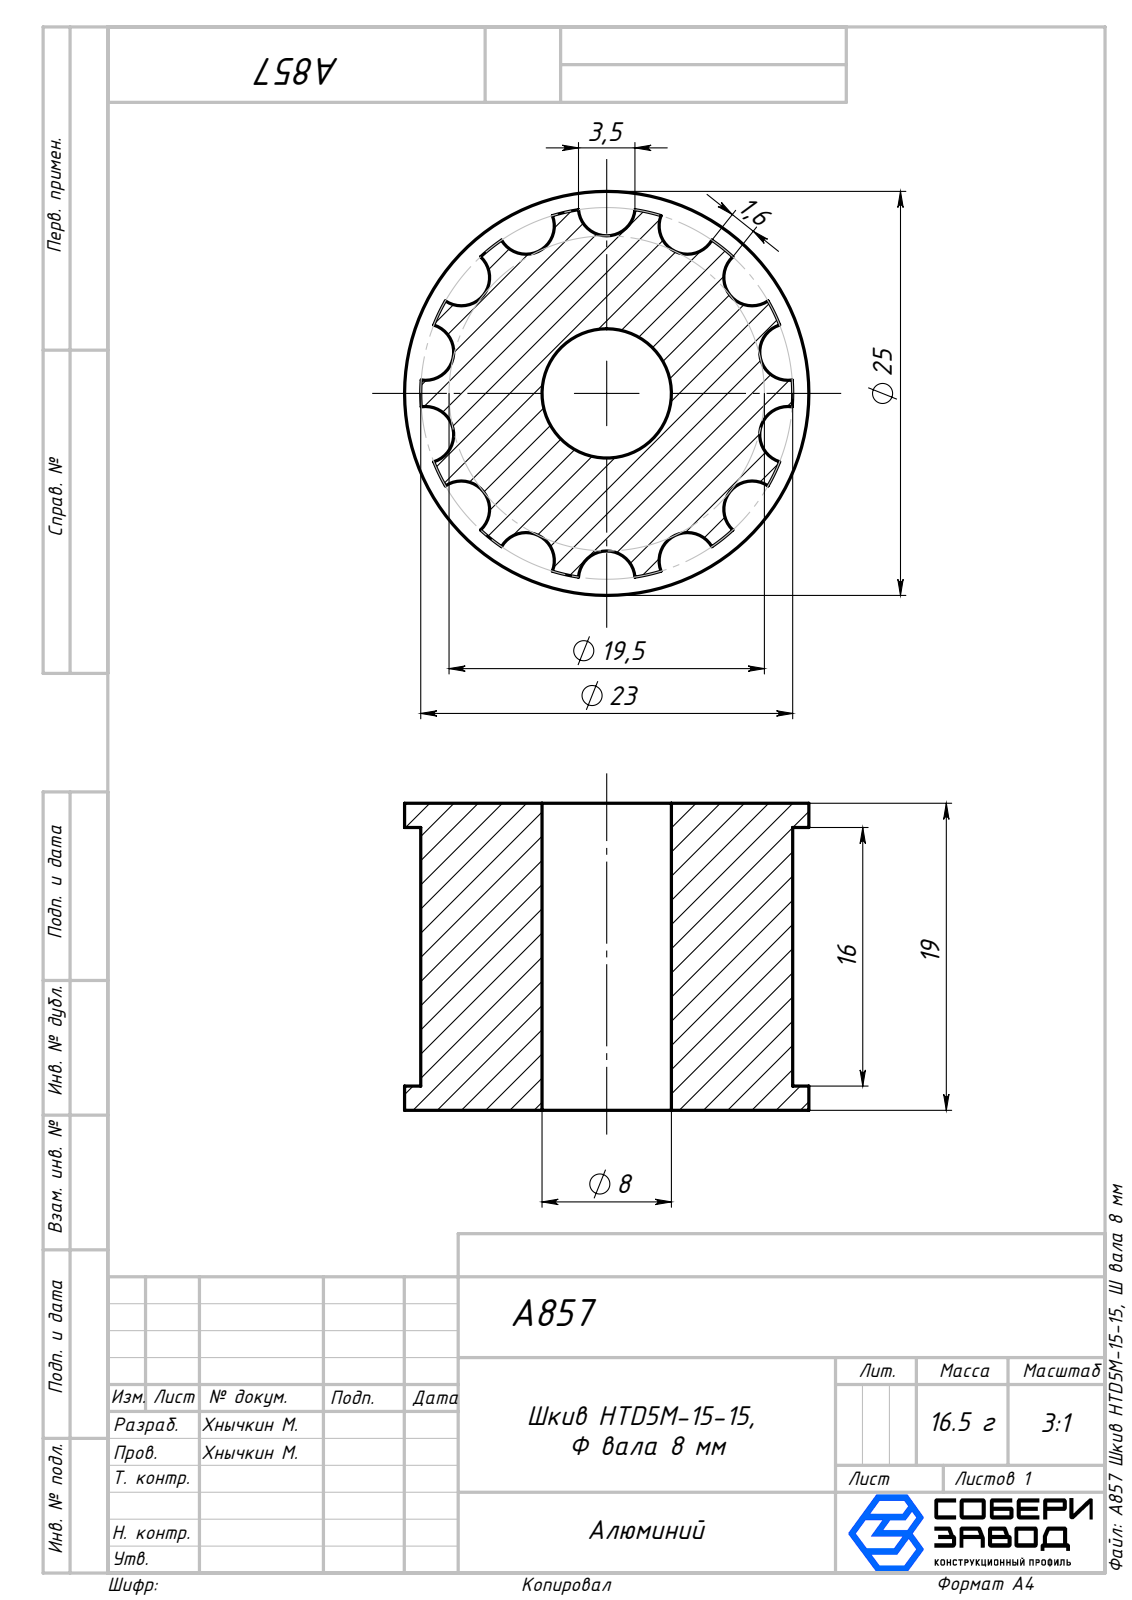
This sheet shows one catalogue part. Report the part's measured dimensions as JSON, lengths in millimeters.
{"part_name": "A857 Шкив HTD5M-15-15, Ø вала 8 мм", "step_written_by": "SolidWorks 2025 (AUTOMOTIVE_DESIGN)", "units": "millimeters", "bodies": {"solids": 1, "faces": 45, "planar": 4, "cylindrical": 41, "other": 0}, "overall_size": [25, 25, 19], "volume_mm3": 6122, "surface_area_mm2": 3419, "round_holes": [[8, 1]], "round_bosses_or_shafts": [[25, 1]], "partial_cylinders_radius": [[1.75, 14], [11.5, 1]], "face_to_face_distances": [19, 1.5, 17.5, 16]}
